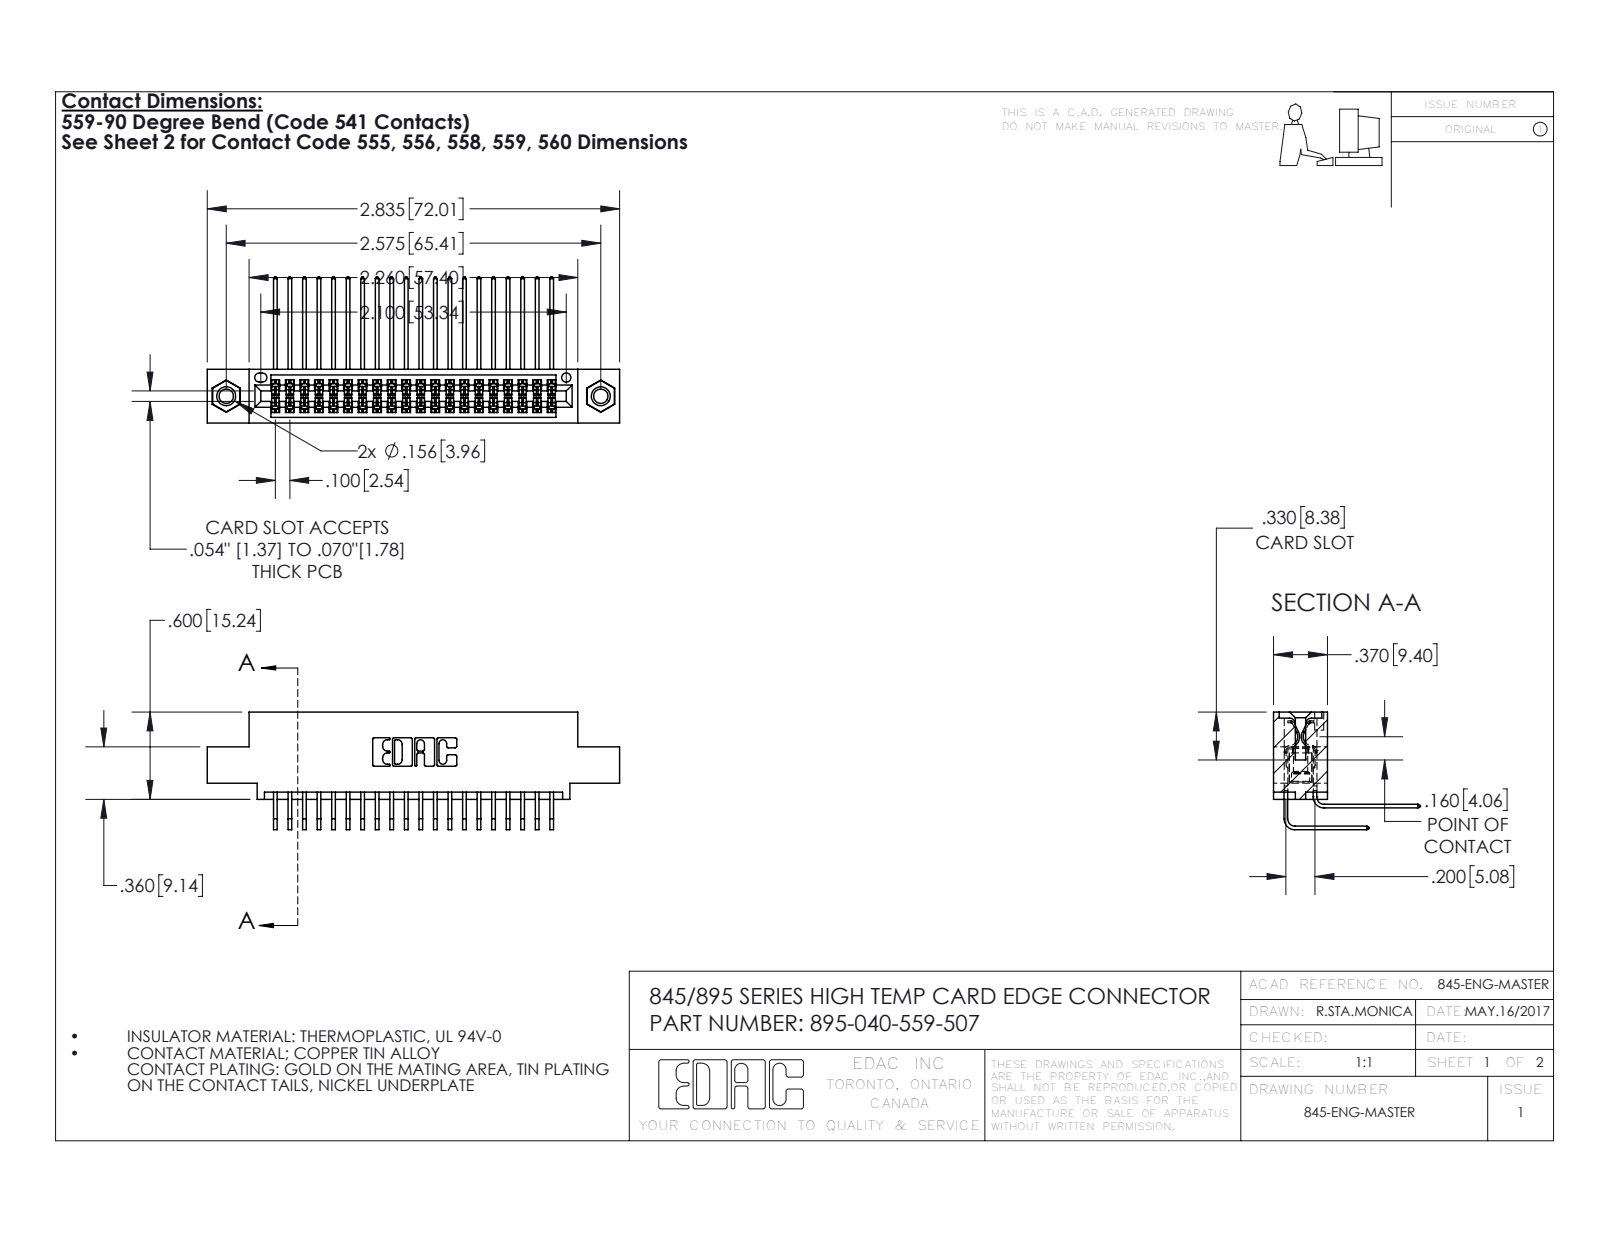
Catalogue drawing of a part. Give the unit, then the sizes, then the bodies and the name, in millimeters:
Units: millimetres
Overall size (bounding box): 72 × 25.5 × 20.5
Round holes (diameter × count): ⌀2.5 ×2, ⌀3.2 ×2, ⌀4 ×2, ⌀1.6 ×1
Round bosses / shafts (diameter × count): ⌀3.9 ×2
Partial cylindrical surfaces — rounded edges, fillets, slot ends (radius × count): R0.2 ×80, R0.3 ×22, R0.2 ×6, R0.8 ×6, R0.7 ×3, R0.4 ×2, R0.5 ×2, R0.6 ×2
Main face-to-face distances: 1.8, 7.6, 5.1, 9.4, 2.5, 6.9, 0.6, 5.7, 3.8, 4.4
Hole centre spacings: 6.9, 59.5, 65.4
Volume: 6 930 mm³ · Surface area: 11 030 mm²
Bodies: 43 solids, 2270 faces (1516 planar, 738 cylindrical, 16 other)
Part name (STEP PRODUCT): 345-250-001_345-250-005-103; 345-292-001_558 559 Tail - 1; 345-292-001_559 Tail - 2; 395-040-559-507 (+1 more)
STEP written by: SolidWorks 2016 (CONFIG_CONTROL_DESIGN)
